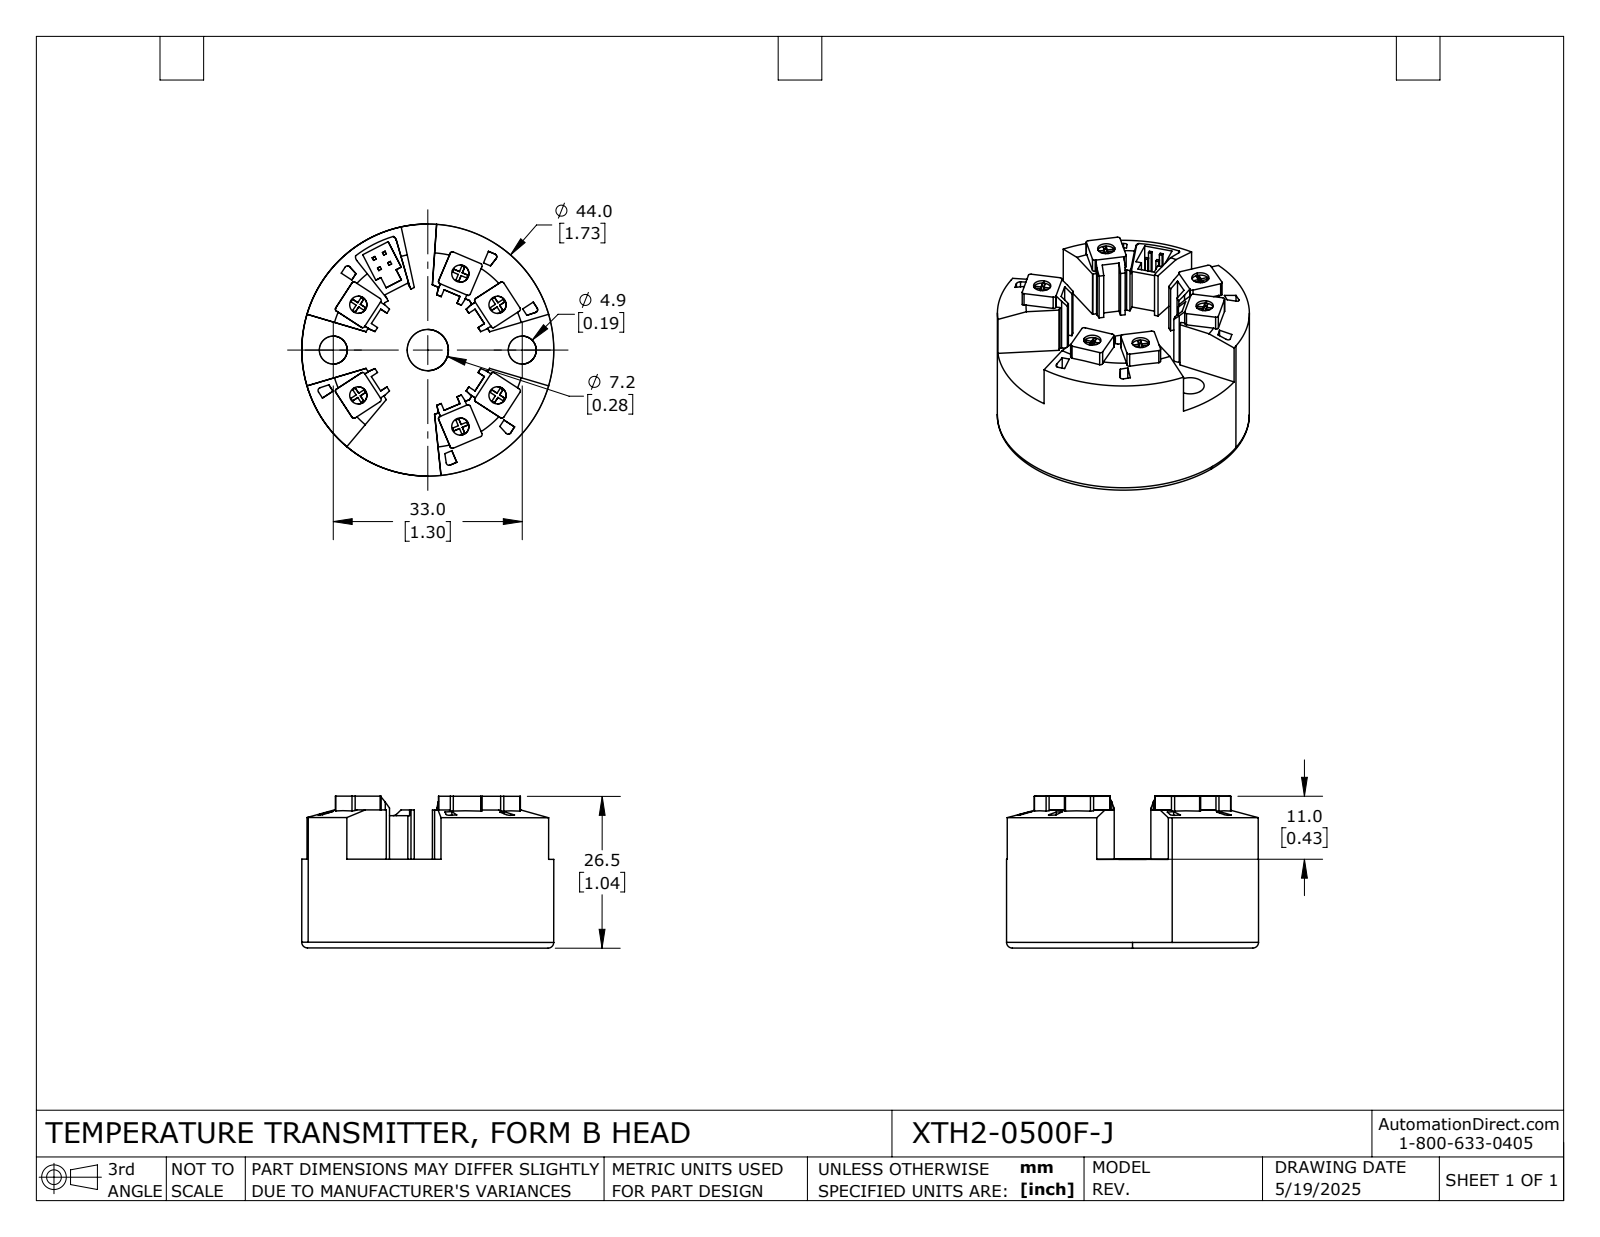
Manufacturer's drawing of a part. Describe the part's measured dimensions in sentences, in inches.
The part is named "XTDH2-0500F-J". Its 3-D file was written by "SolidWorks 2024 (AUTOMOTIVE_DESIGN)". It is 1 solid with 341 faces: 281 planar, 52 cylindrical and 8 other. Overall it measures 1.733 by 1.732 by 1.045 inches. Its volume is 1.748 cubic inches and its surface area 13.46 square inches. Round holes: 6 of diameter 0.118, 2 of diameter 0.193, 1 of diameter 0.283. Round bosses or shafts: 1 of diameter 1.732. Partial cylindrical surfaces (rounded edges, fillets, slot ends): 24 of radius 0.016, 6 of radius 0.02, 2 of radius 0.039. The main face-to-face distances are 0.61, 1.043, 0.433, 0.059, 0.177, 0.039, 0.02, 0.118, 0.949, 0.339. The hole center spacings are 0.571, 0.333, 0.355, 0.356, 0.65, 0.677, 0.733, 0.875.
